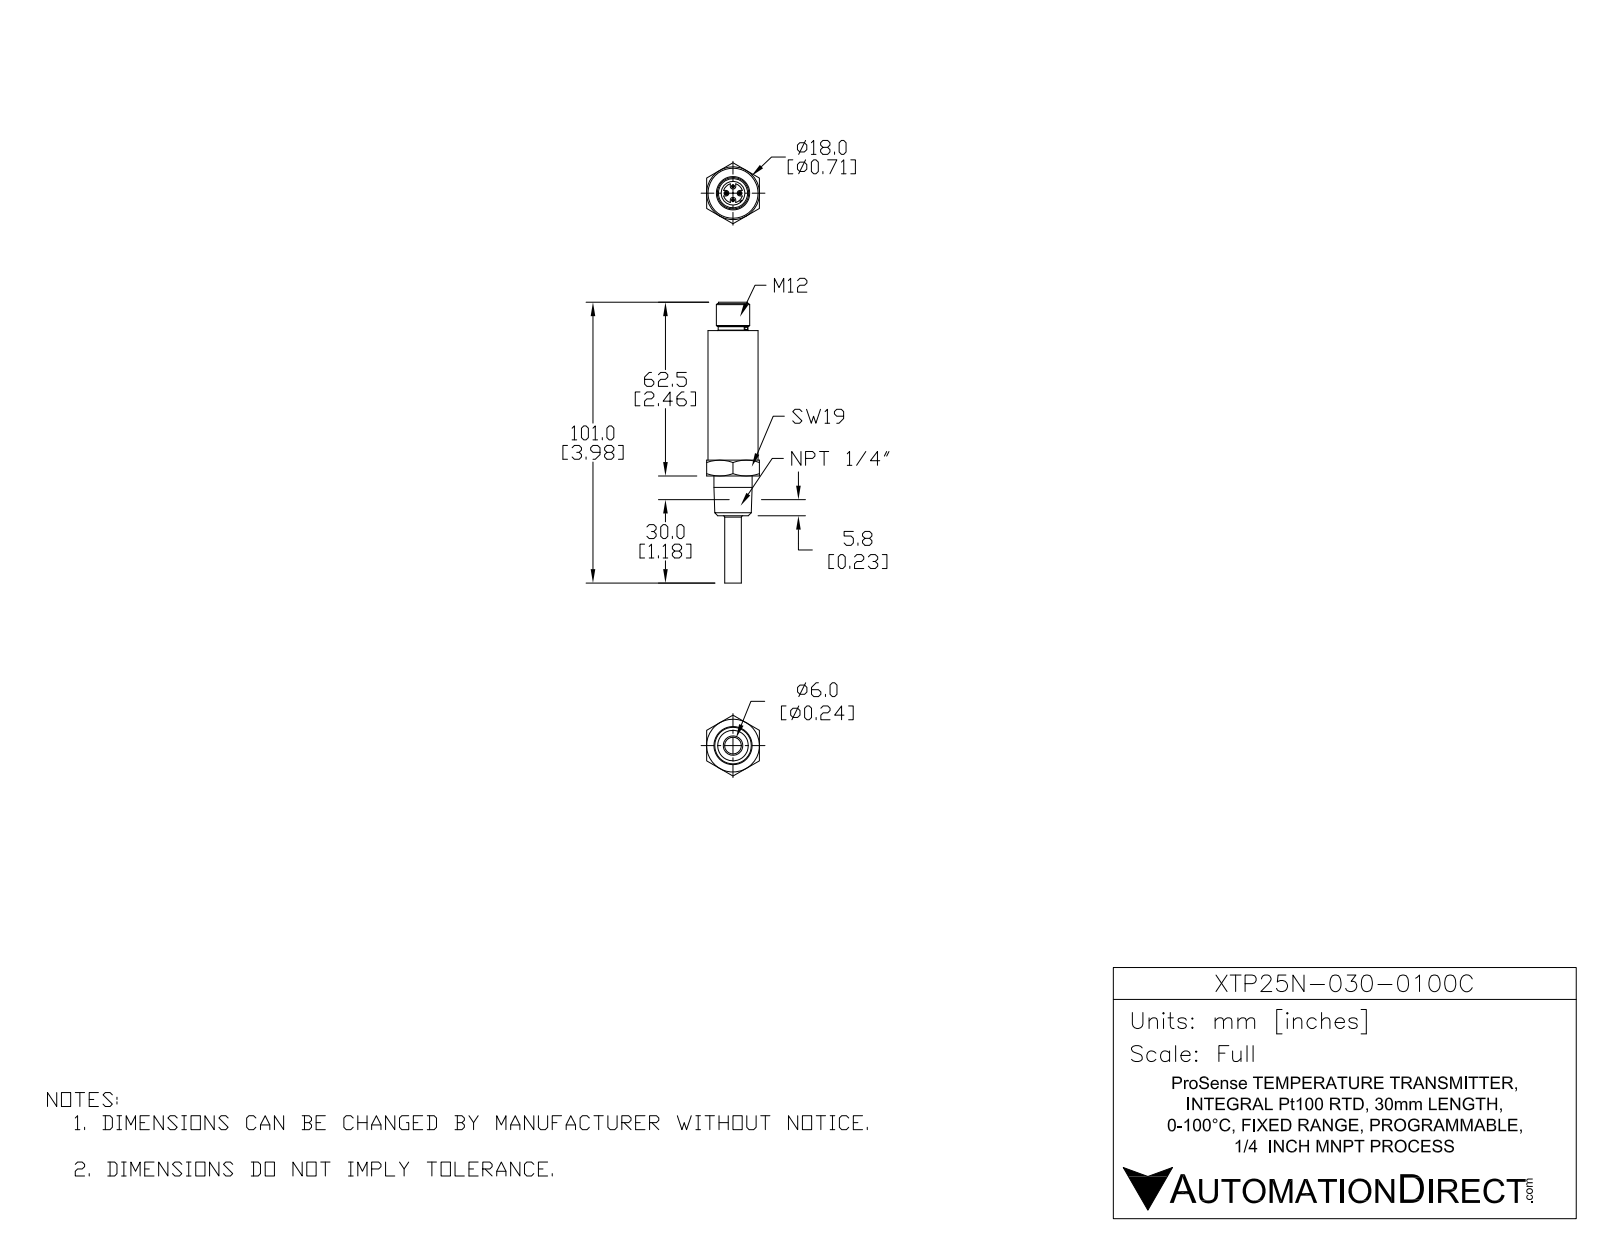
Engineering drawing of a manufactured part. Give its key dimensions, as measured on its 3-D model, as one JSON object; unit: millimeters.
{"part_name": "XTP25N-030-0100C", "step_written_by": "SolidWorks 2015 (AUTOMOTIVE_DESIGN)", "units": "millimeters", "bodies": {"solids": 1, "faces": 117, "planar": 43, "cylindrical": 34, "other": 40}, "overall_size": [101, 21.94, 19], "volume_mm3": 16667, "surface_area_mm2": 5627, "round_holes": [[4, 1], [8.5, 1]], "round_bosses_or_shafts": [[1.02, 4], [18, 1], [13.72, 1], [12, 1], [10.7, 1], [10.5, 1], [6, 1]], "partial_cylinders_radius": [[1, 4], [3.5, 1], [4.25, 1]], "face_to_face_distances": [19, 52.3, 14.3, 66.6, 20, 5.7, 46.6, 76.8, 62.5, 56.8]}
